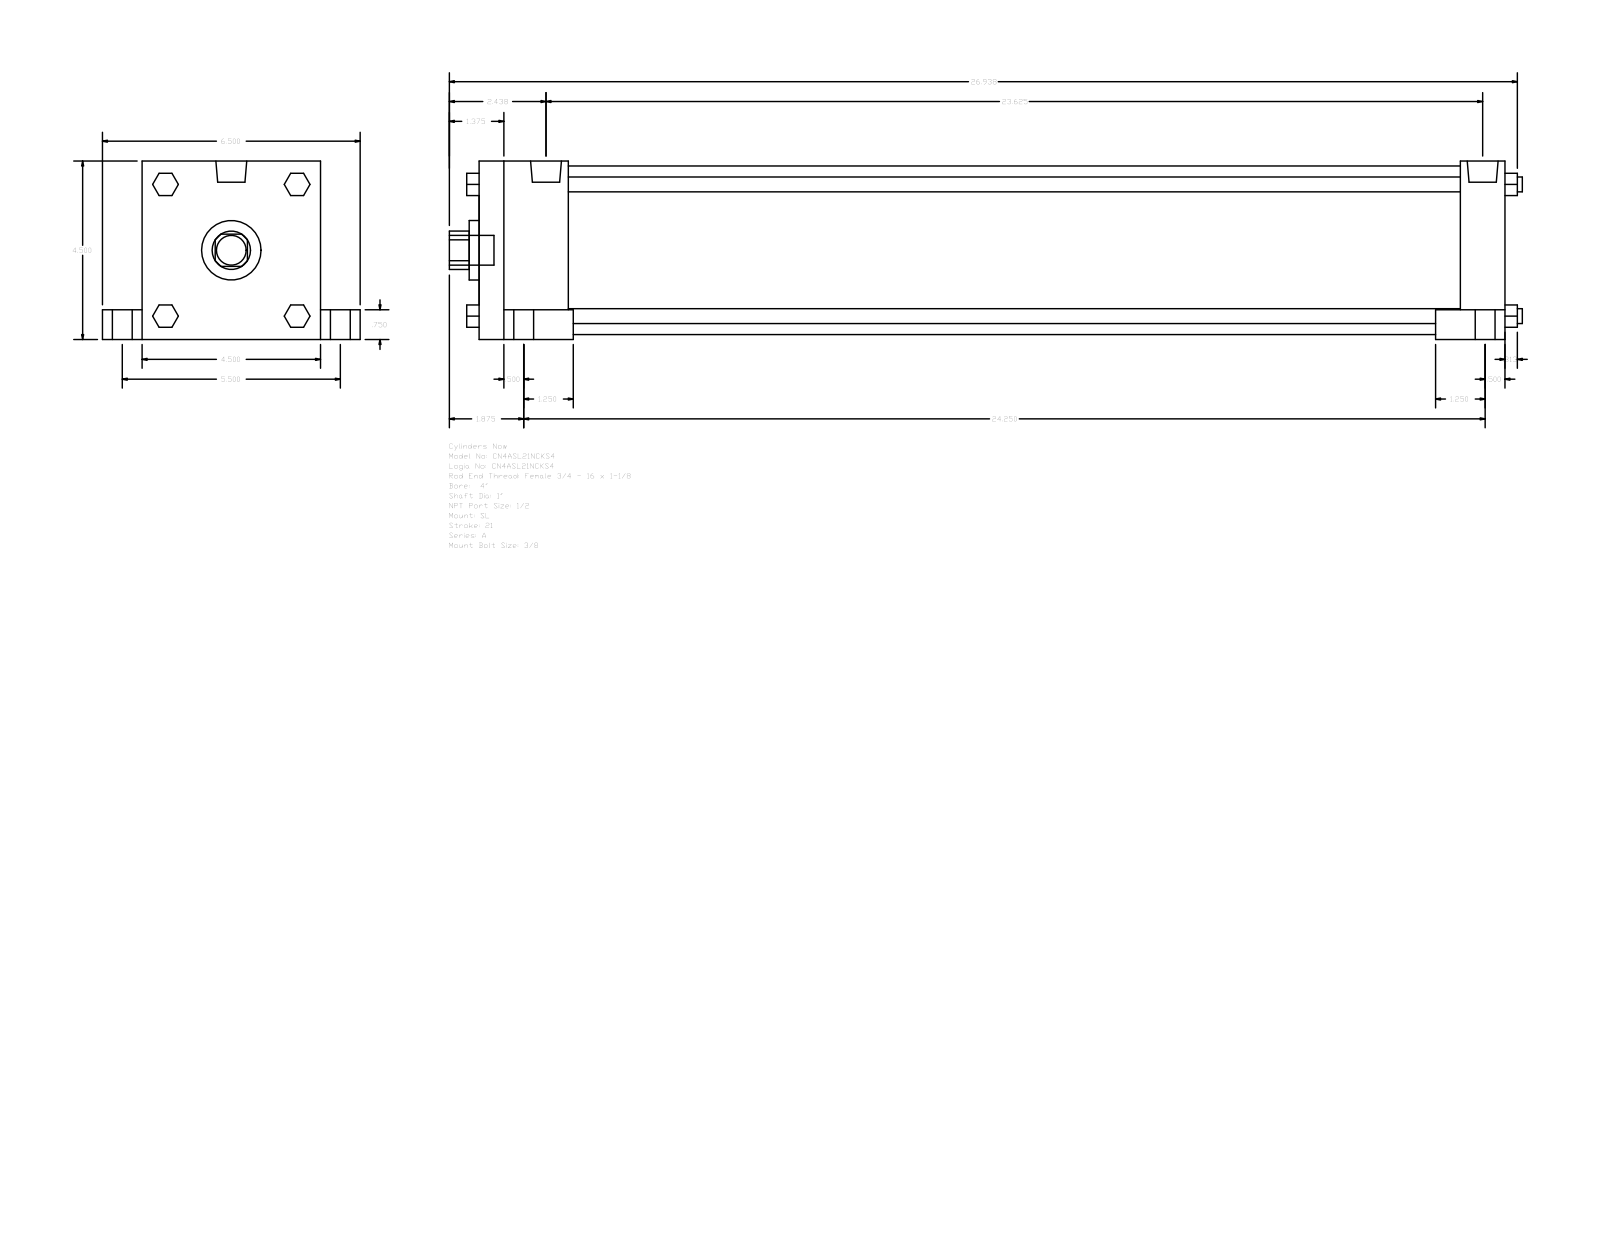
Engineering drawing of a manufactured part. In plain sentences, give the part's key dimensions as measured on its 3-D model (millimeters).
The part is named "A_SL__0400_1". Its 3-D file was written by "GSSL Pune (CONFIG_CONTROL_DESIGN)". It is 0 solids with 150 faces: 114 planar, 36 cylindrical and 0 other. Overall it measures 687.39 by 165.1 by 114.3 millimeters. Round holes: 1 of diameter 25.4, 1 of diameter 38.1, 1 of diameter 107.95. Round bosses or shafts: 5 of diameter 19.05, 4 of diameter 12.7, 4 of diameter 9.53, 4 of diameter 8.73, 2 of diameter 19.77. Partial cylindrical surfaces (rounded edges, fillets, slot ends): 1 of radius 12.29. The main face-to-face distances are 114.3, 657.22, 28.57, 57.15, 600.07, 628.65, 571.5, 19.05, 25.4, 139.7.
